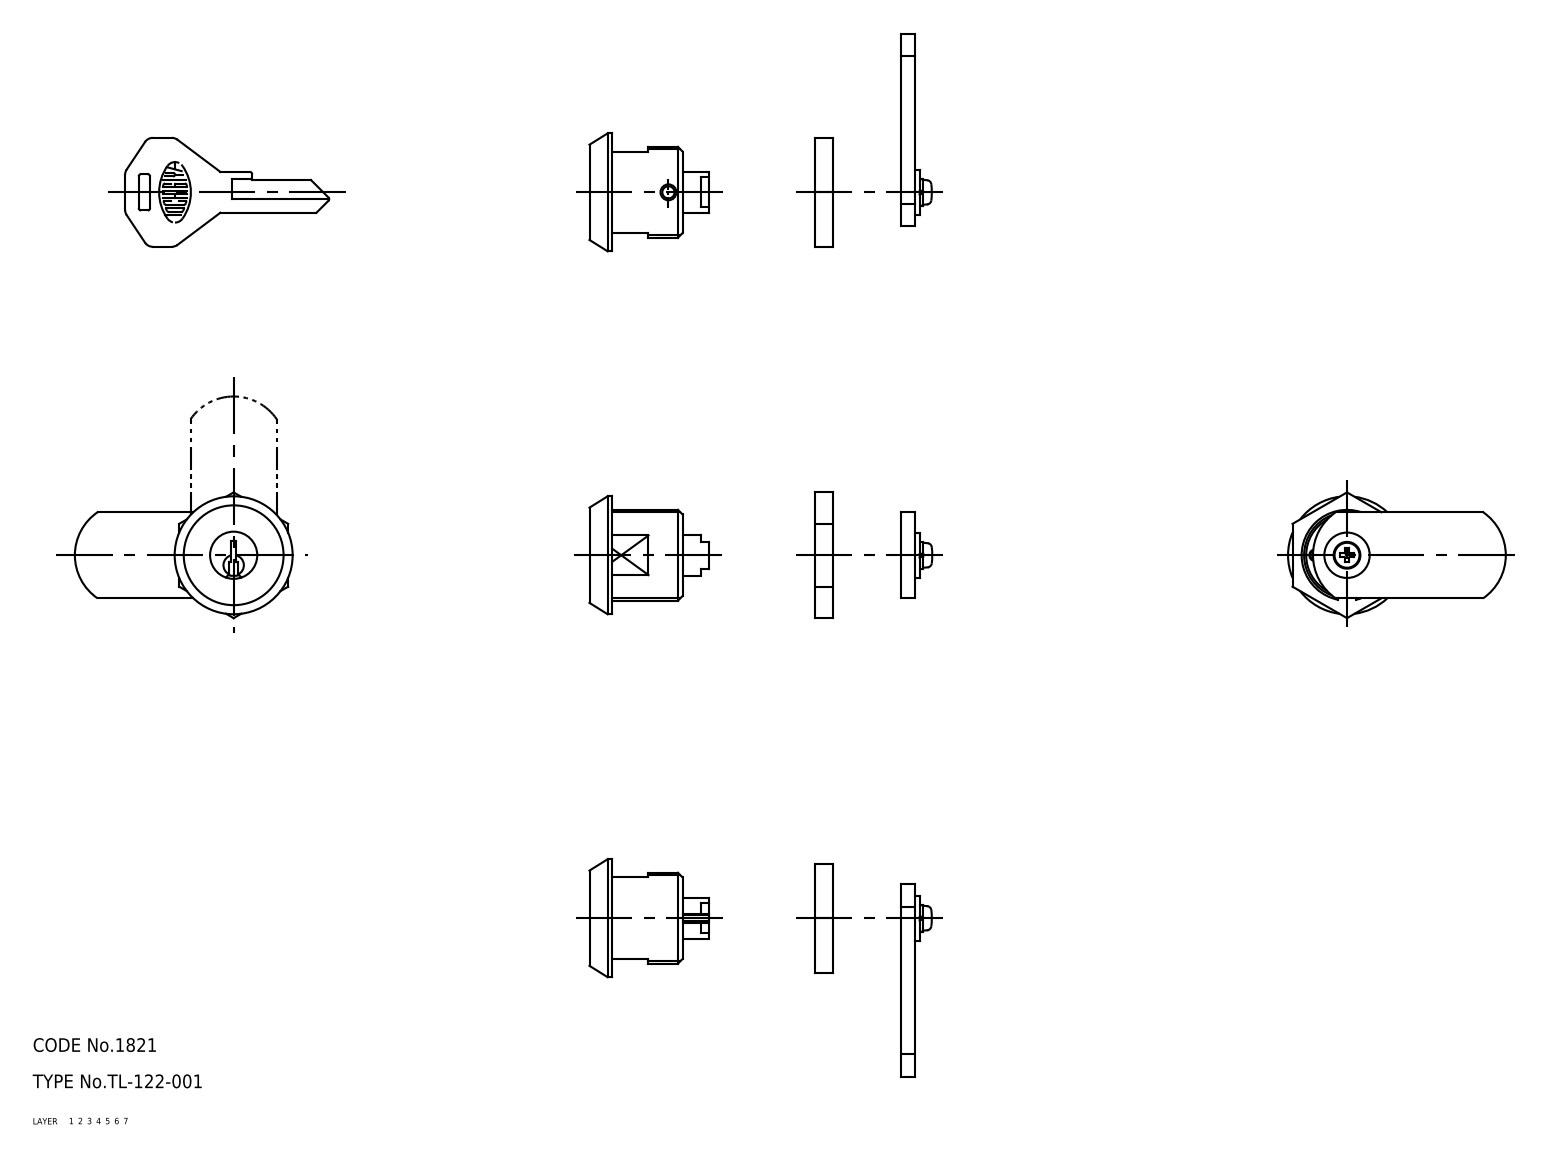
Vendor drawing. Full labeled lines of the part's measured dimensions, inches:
Part name (STEP PRODUCT): screw; nut_2; nut_1; lock (+3 more)
STEP written by: CADfix (AUTOMOTIVE_DESIGN)
Units: inches
Bodies: 8 solids, 150 faces (0 planar, 0 cylindrical, 150 other)
Overall size (bounding box): 3.76 × 1.89 × 1.091
Volume: 0.677 in³ · Surface area: 13.06 in²
